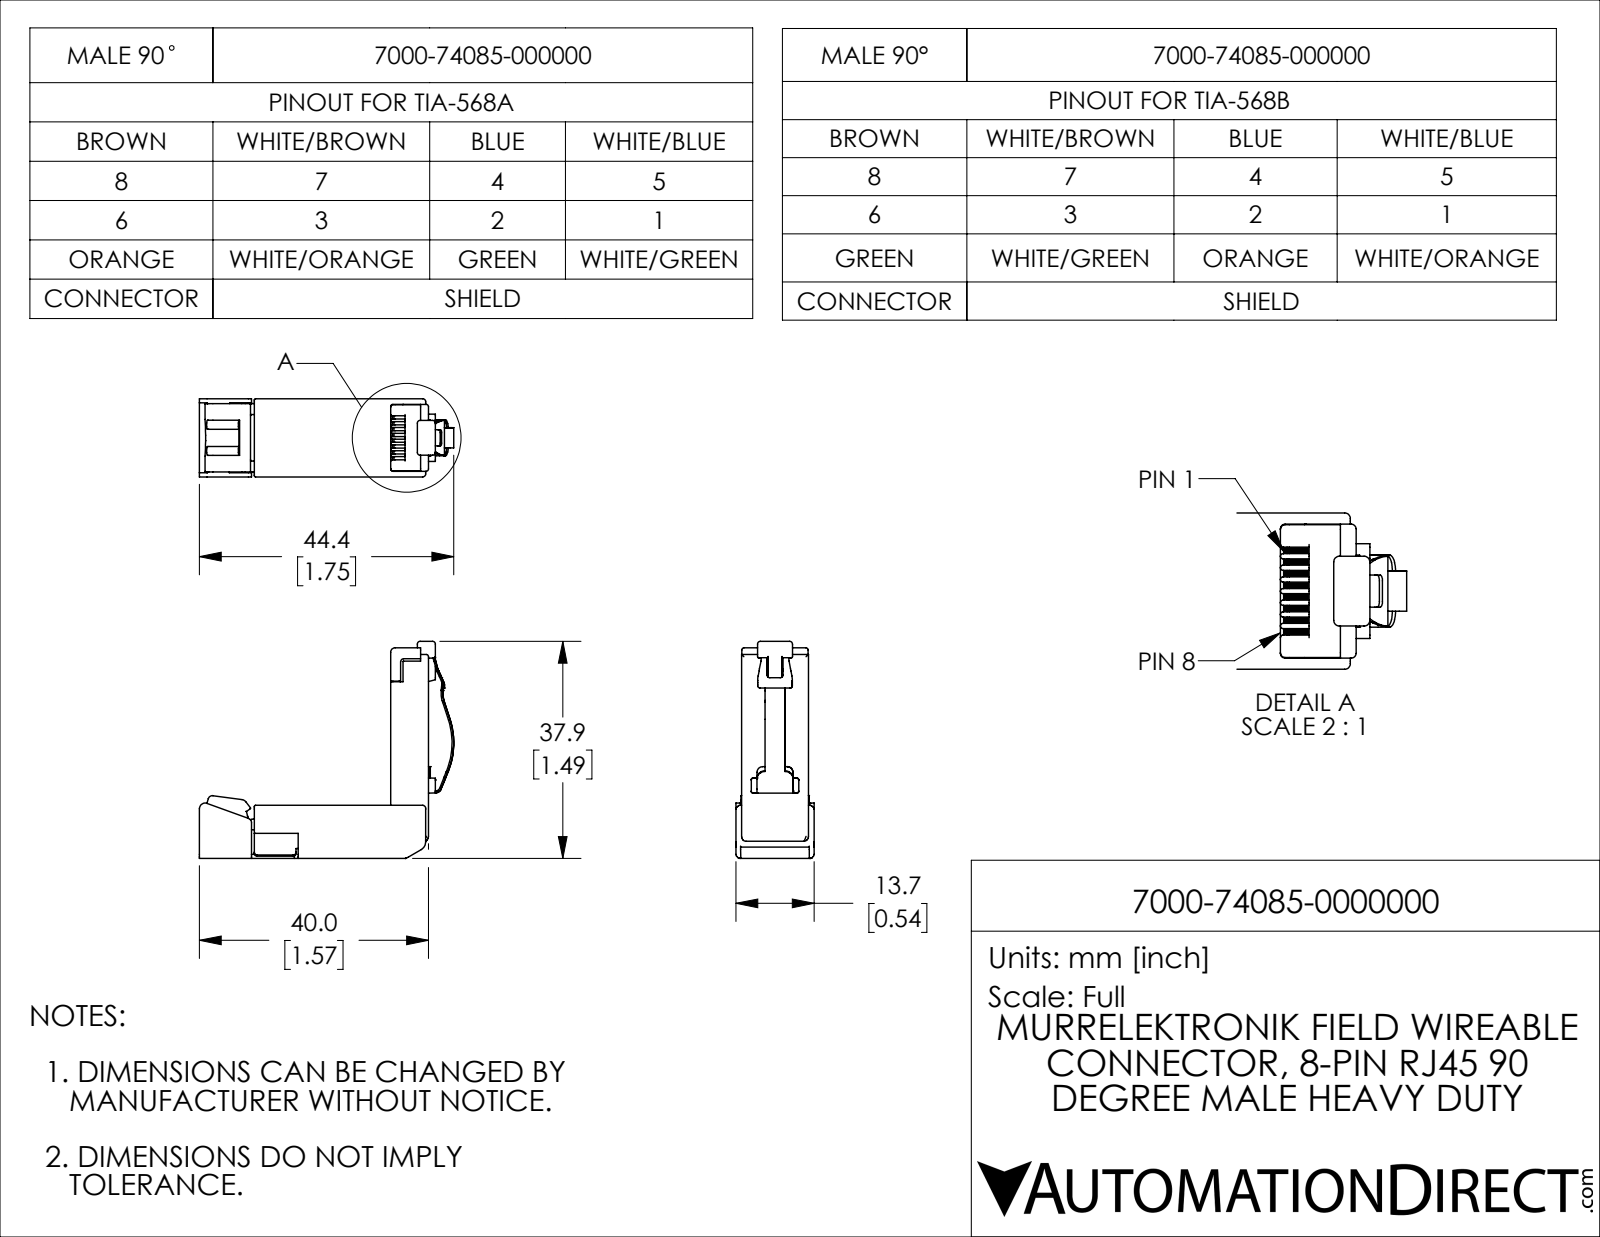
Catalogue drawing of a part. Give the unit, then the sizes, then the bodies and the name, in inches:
Units: inches
Overall size (bounding box): 1.749 × 1.492 × 0.537
Partial cylindrical surfaces — rounded edges, fillets, slot ends (radius × count): R0.02 ×39, R0.004 ×20, R0.012 ×19, R0.009 ×18, R0.016 ×13, R0.039 ×9, R0.008 ×6, R0.024 ×3
Main face-to-face distances: 0.365, 0.537, 0.26, 0.039, 0.498, 0.499, 0.46, 0.039, 0.029, 0.509
Volume: 0.391 in³ · Surface area: 6.21 in²
Bodies: 1 solid, 507 faces (226 planar, 189 cylindrical, 92 other)
Part name (STEP PRODUCT): 7000-74085-0000000
STEP written by: SolidWorks 2021 (CONFIG_CONTROL_DESIGN)
